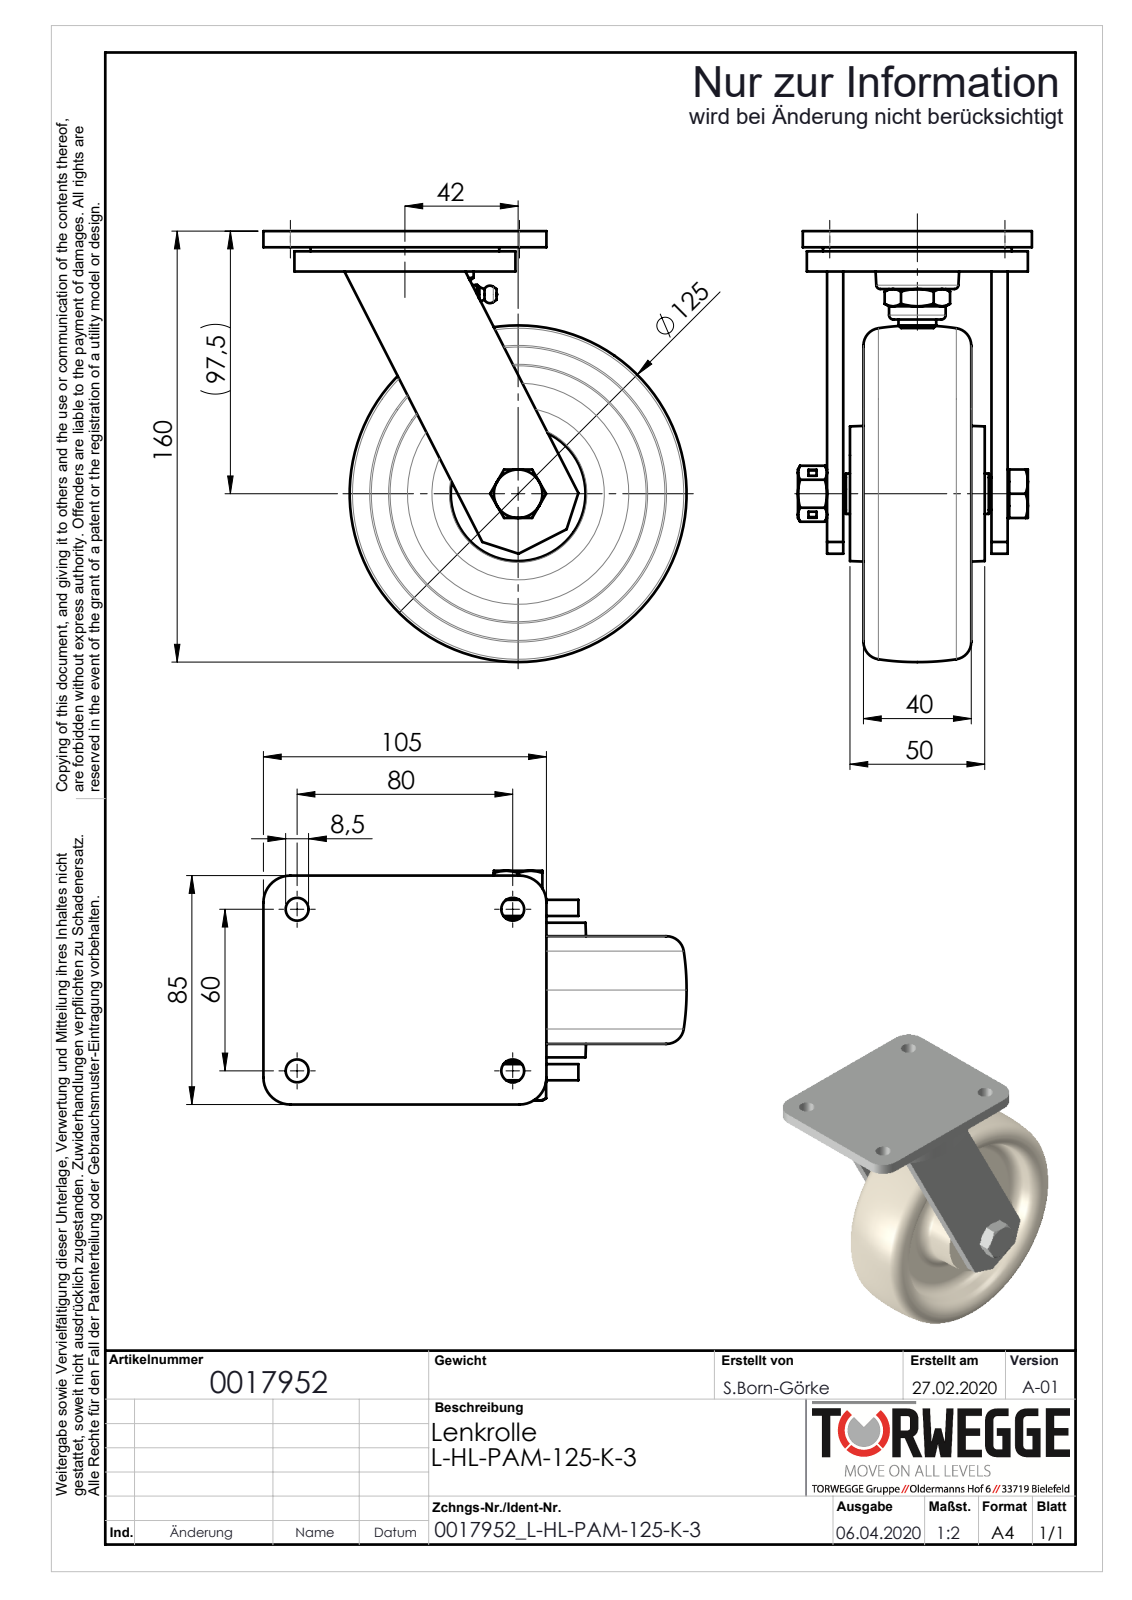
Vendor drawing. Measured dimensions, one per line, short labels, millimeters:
name: 0017952
written by: SolidWorks 2018 (AUTOMOTIVE_DESIGN)
unit: mm
bodies: 19 solids, 373 faces (125 planar, 108 cylindrical, 140 other)
size: 160 × 157 × 86.8
volume: 496 389 mm³; area: 129 111 mm²
holes: 4× ⌀8.5, 2× ⌀12, 2× ⌀16, 1× ⌀5, 1× ⌀10.2, 1× ⌀12.2, 1× ⌀14, 1× ⌀15, 1× ⌀20.3, 1× ⌀28.48, 1× ⌀29.7, 1× ⌀30
bosses: 1× ⌀82, 1× ⌀70, 1× ⌀35, 1× ⌀21.52, 1× ⌀21, 1× ⌀20, 1× ⌀18, 1× ⌀6
rounds: 4× R10
face distances: 6, 61, 9, 28.5, 15, 55, 67, 22.5, 38.5, 32.5
hole spacings: 50, 35.51, 60, 67.98, 80, 100, 21
